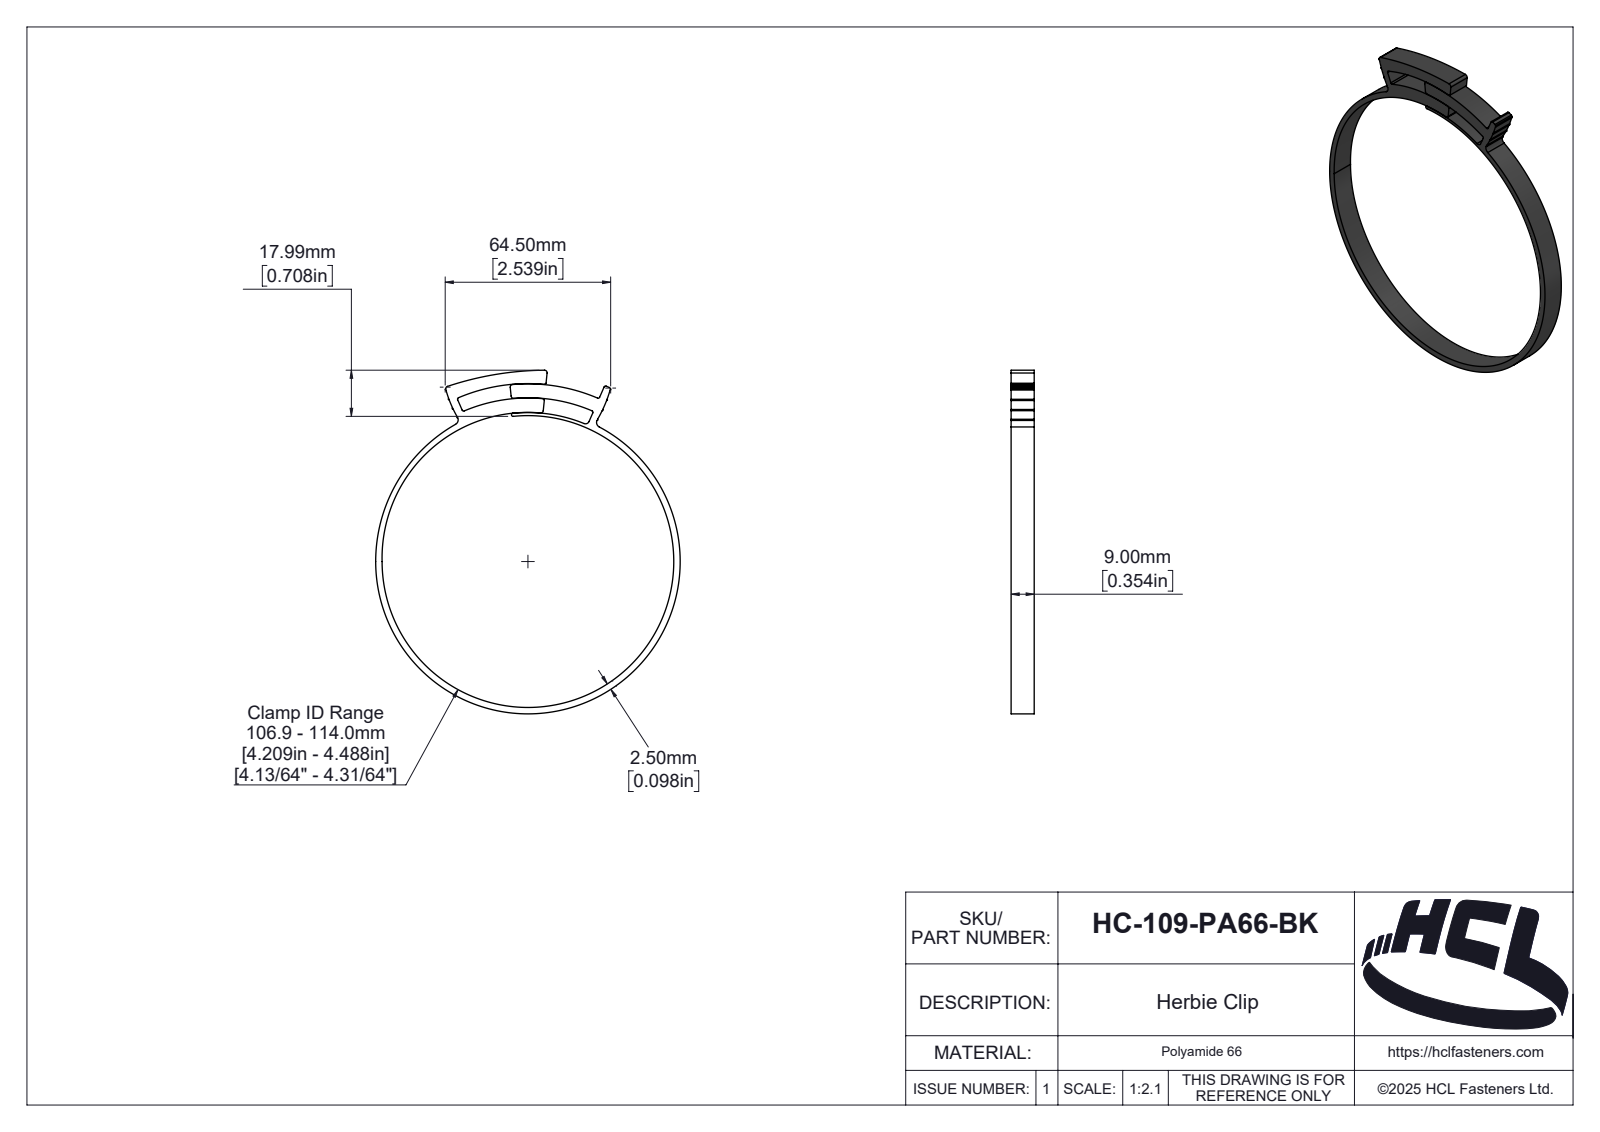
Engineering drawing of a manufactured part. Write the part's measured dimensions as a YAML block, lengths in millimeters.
part_name: "HC-109-PA66-BK"
step_written_by: "SolidWorks 2025 (AUTOMOTIVE_DESIGN)"
units: millimeters
bodies: {solids: 1, faces: 162, planar: 13, cylindrical: 100, other: 49}
overall_size: [133.9, 118.7, 9]
volume: 12994
surface_area: 11534
partial_cylinders:
  - {radius: 0.25, count: 8}
  - {radius: 0.6, count: 7}
  - {radius: 1, count: 5}
  - {radius: 2, count: 2}
  - {radius: 0.17, count: 1}
  - {radius: 0.67, count: 1}
  - {radius: 0.84, count: 1}
  - {radius: 0.89, count: 1}
face_to_face_distances: [9]
